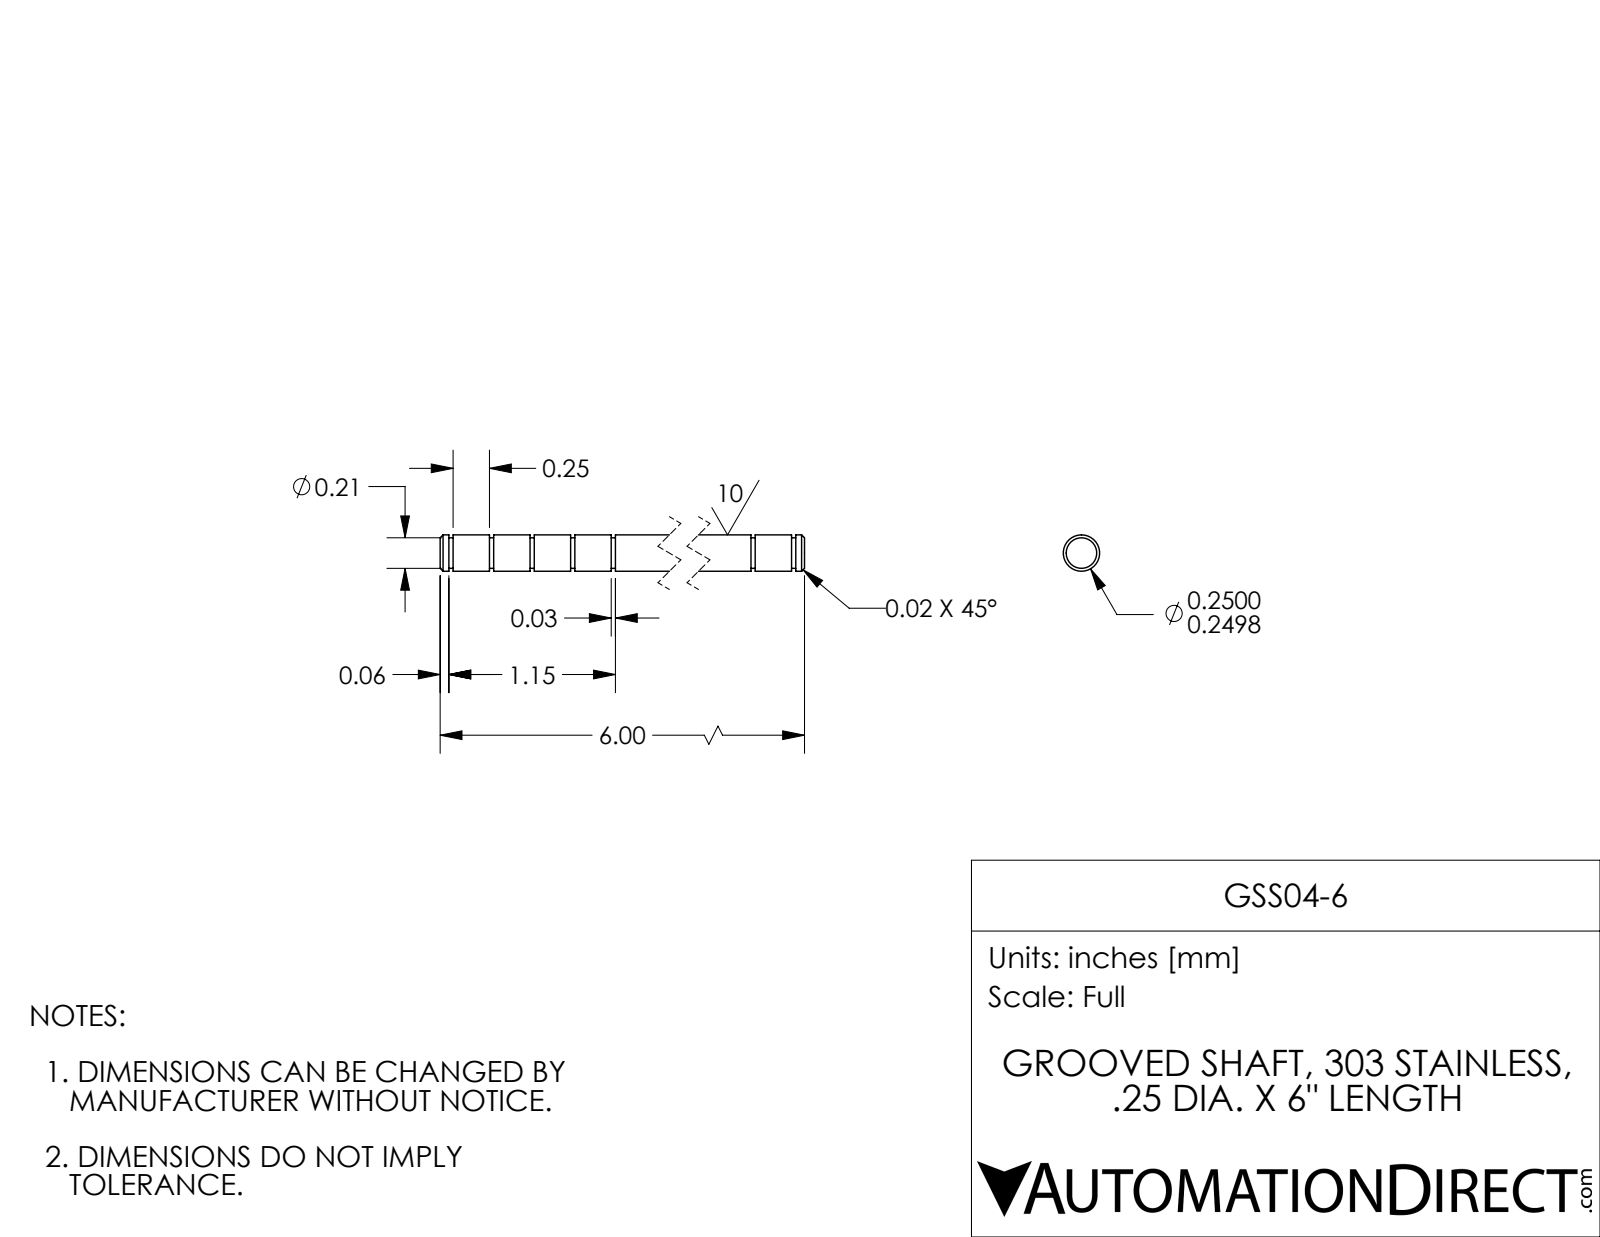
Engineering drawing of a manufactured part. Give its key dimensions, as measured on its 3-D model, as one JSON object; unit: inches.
{"part_name": "GSS04-6", "step_written_by": "SolidWorks 2017 (AUTOMOTIVE_DESIGN)", "units": "inches", "bodies": {"solids": 1, "faces": 50, "planar": 16, "cylindrical": 30, "other": 4}, "overall_size": [6, 0.25, 0.25], "volume_in3": 0.291, "surface_area_in2": 4.968, "round_bosses_or_shafts": [[0.25, 1], [0.21, 1]], "face_to_face_distances": [0.279, 0.029, 0.25, 0.837, 5.572, 0.558, 4.735, 5.293, 5.014, 0.308]}
